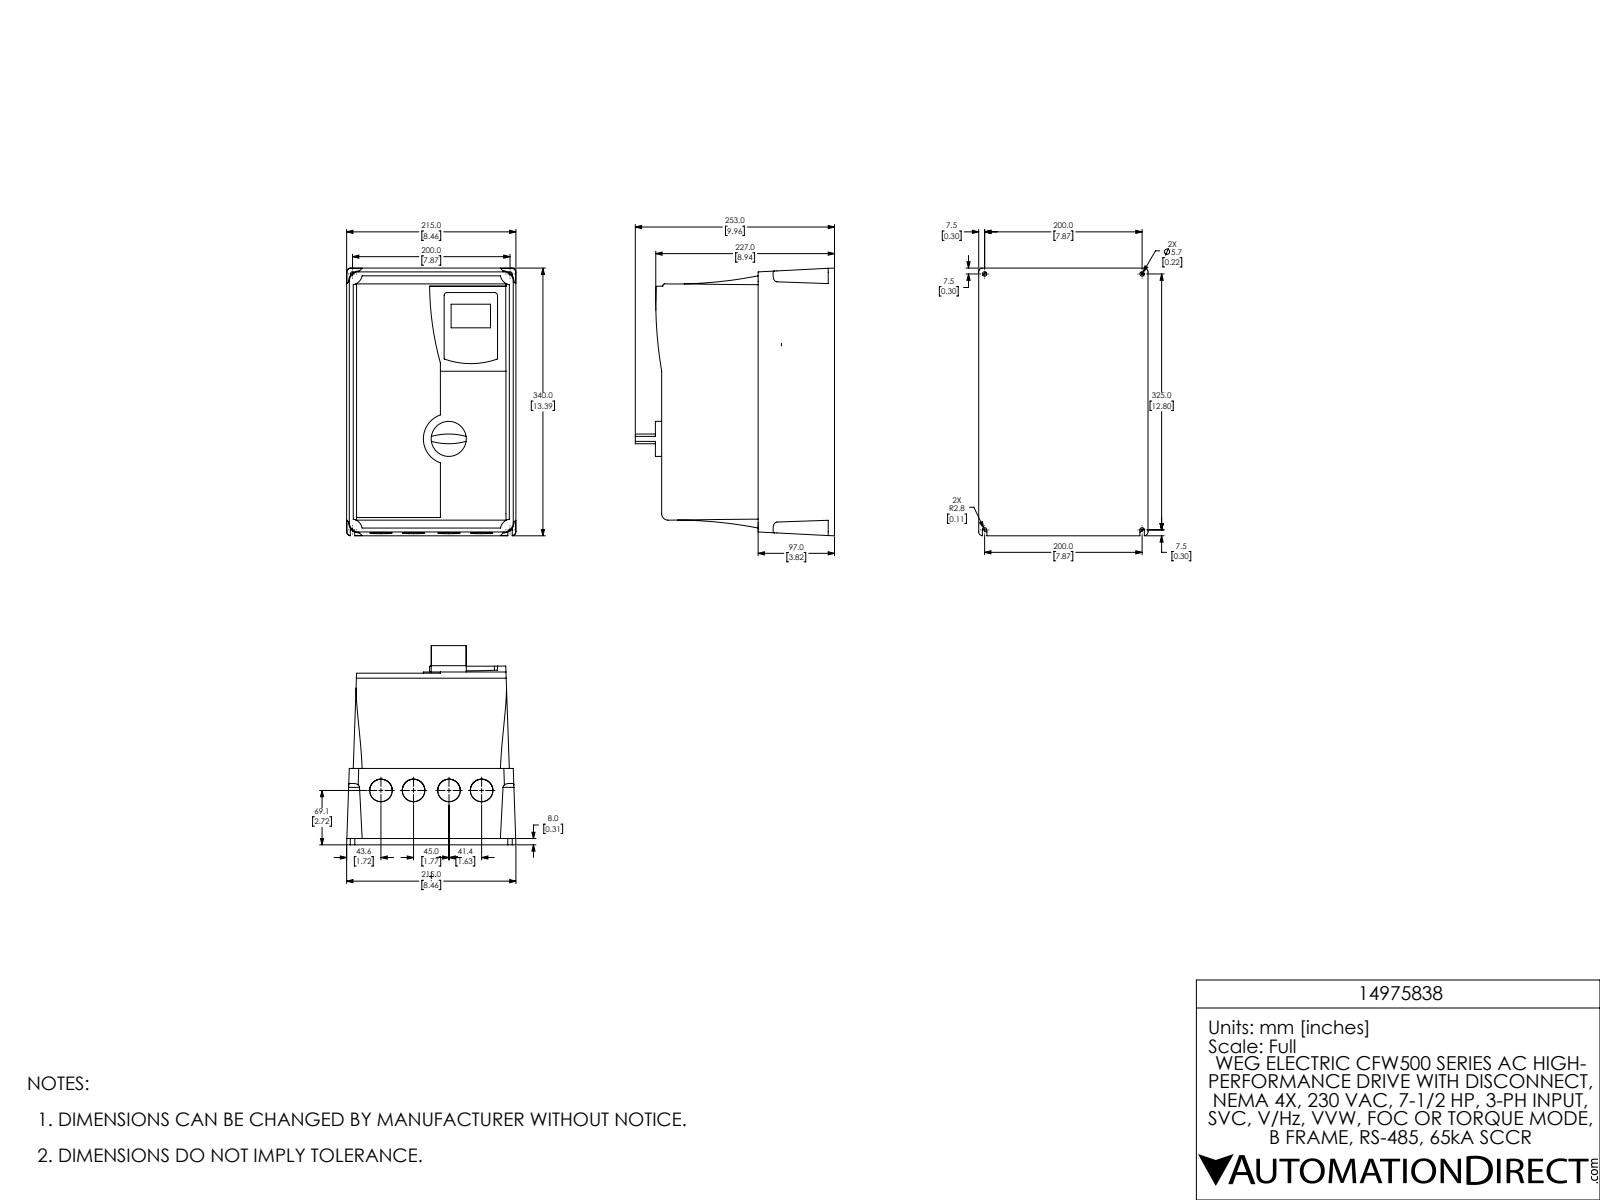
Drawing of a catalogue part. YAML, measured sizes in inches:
part_name: "CFW500 MEC-B IP66 - COM SECCIONADORA Coord NC"
step_written_by: "SolidWorks 2017 (AUTOMOTIVE_DESIGN)"
units: inches
bodies: {solids: 1, faces: 91, planar: 43, cylindrical: 46, other: 2}
overall_size: [13.386, 9.961, 8.465]
volume: 859.6
surface_area: 571.1
round_holes:
  - {diameter: 1.126, count: 4}
  - {diameter: 0.223, count: 2}
round_bosses_or_shafts:
  - {diameter: 1.753, count: 1}
partial_cylinders:
  - {radius: 0.197, count: 6}
  - {radius: 0.472, count: 4}
  - {radius: 0.551, count: 4}
  - {radius: 0.033, count: 2}
  - {radius: 0.111, count: 2}
  - {radius: 0.152, count: 2}
  - {radius: 3.23, count: 2}
  - {radius: 0.079, count: 1}
face_to_face_distances: [0.196, 8.583, 8.642, 0.059, 3.819, 4.764, 4.823, 14.335, 0.315, 0.118]
hole_center_spacings: [1.63, 3.402, 1.772, 5.032, 7.874]
